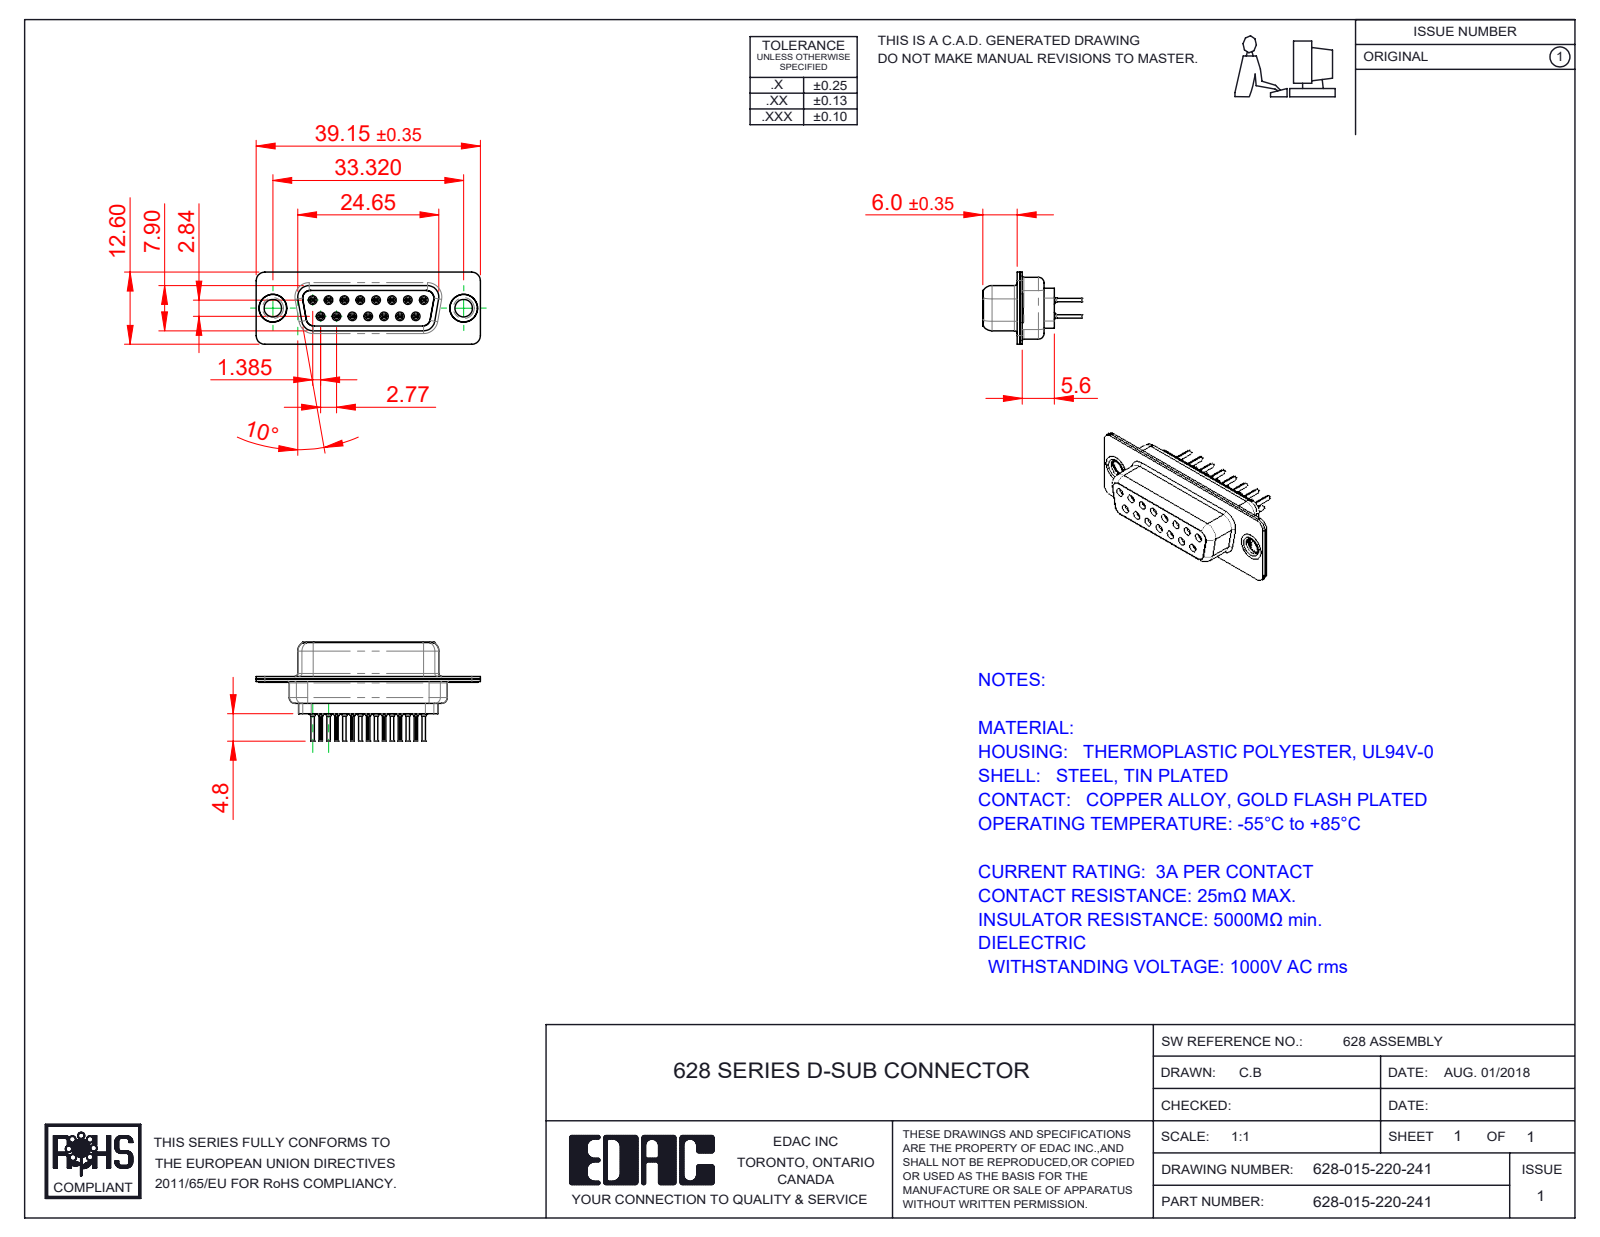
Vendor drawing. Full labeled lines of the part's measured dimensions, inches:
Part name (STEP PRODUCT): 628 Contact Row 2_20L; 628 Shell Front_15 Contacts; 628 Housing_15 LP; 628 Contact Row 1_20L (+3 more)
STEP written by: SolidWorks 2020 (CONFIG_CONTROL_DESIGN)
Units: inches
Bodies: 20 solids, 2158 faces (532 planar, 616 cylindrical, 1010 other)
Overall size (bounding box): 1.541 × 0.681 × 0.496
Volume: 0.15 in³ · Surface area: 9.581 in²
Round holes (diameter × count): ⌀0.008 ×15, ⌀0.031 ×15, ⌀0.035 ×15, ⌀0.043 ×15, ⌀0.063 ×15, ⌀0.067 ×8, ⌀0.12 ×2, ⌀0.157 ×2, ⌀0.159 ×2, ⌀0.191 ×2
Round bosses / shafts (diameter × count): ⌀0.079 ×15, ⌀0.059 ×15, ⌀0.047 ×15, ⌀0.024 ×15, ⌀0.197 ×2, ⌀0.195 ×2, ⌀0.189 ×2, ⌀0.14 ×2
Partial cylindrical surfaces — rounded edges, fillets, slot ends (radius × count): R0.004 ×30, R0.059 ×18, R0.011 ×15, R0.079 ×12, R0.053 ×8, R0.01 ×4, R0.02 ×4, R0.024 ×4
Main face-to-face distances: 0.018, 0.016, 0.035, 0.26, 0.075, 0.335, 0.055, 0.278, 0.033, 0.293
Hole centre spacings: 0.124, 0.109, 0.218, 0.327, 0.436, 0.198, 0.198, 0.294
